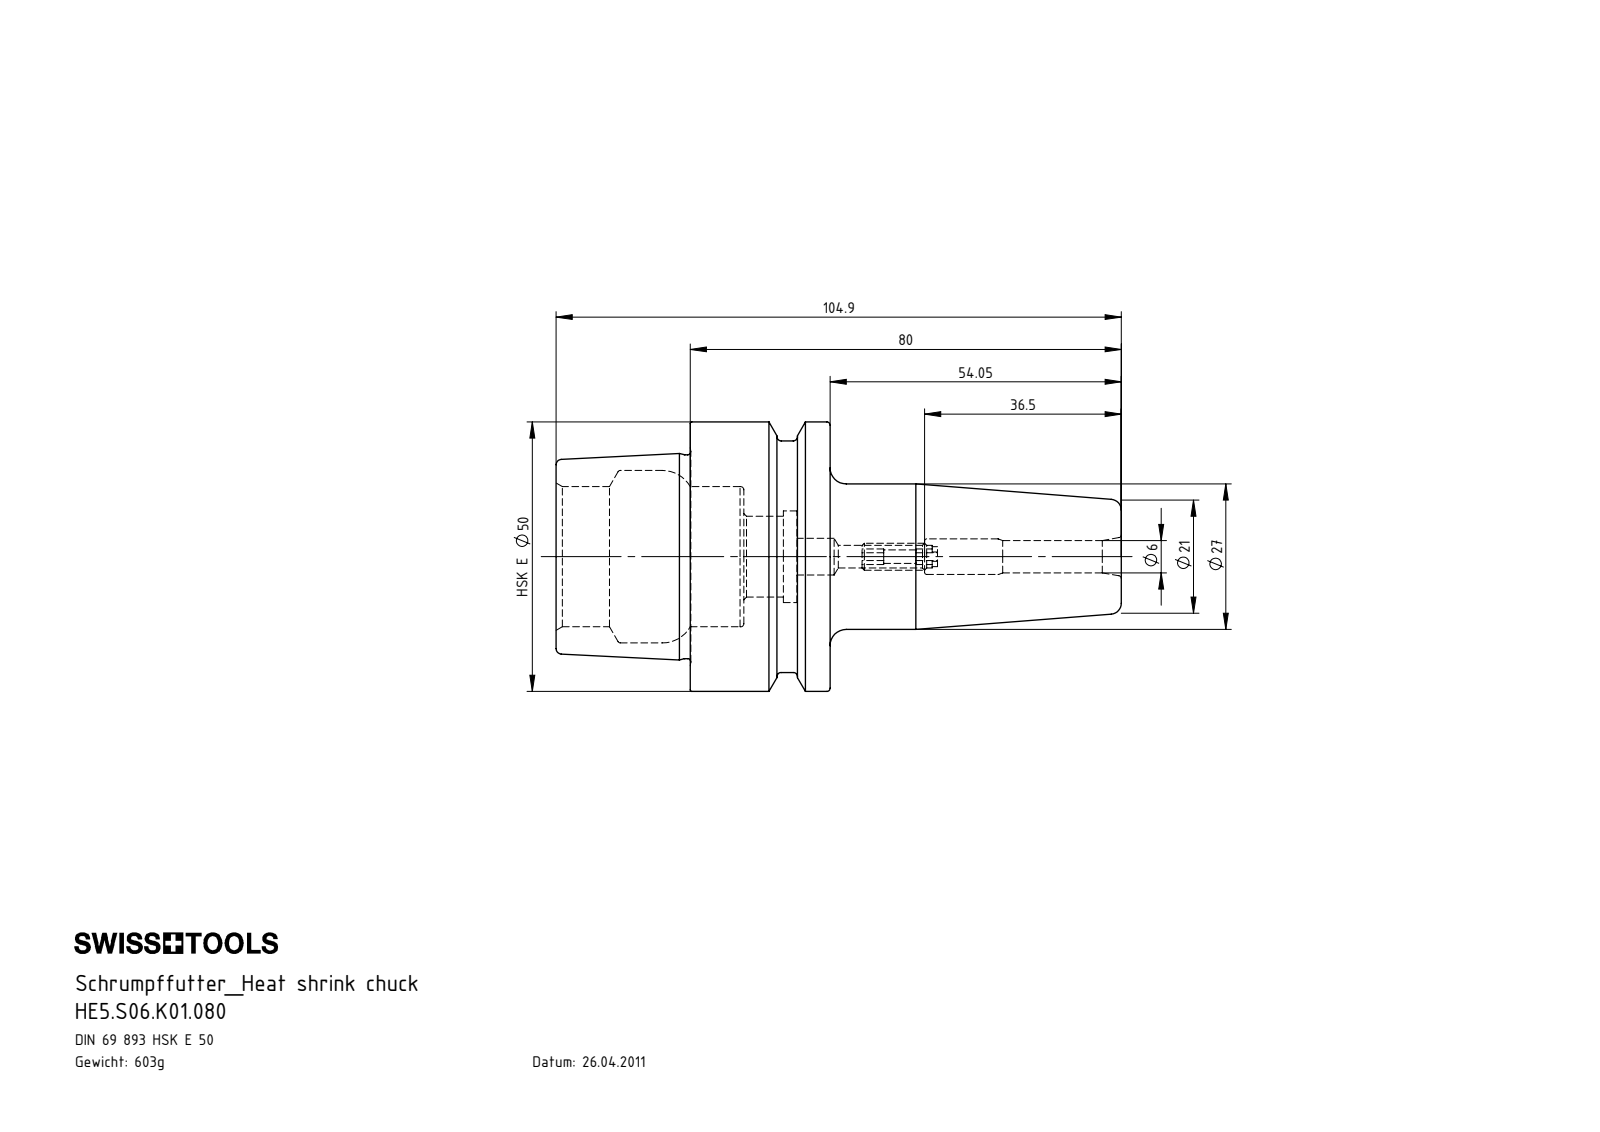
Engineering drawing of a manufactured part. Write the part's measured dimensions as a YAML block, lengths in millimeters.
part_name: "HE5.S06.K01.080; ERU-AN1.K01.014_A; HE5-S06.K01.080_B_Fertigbearbeitung"
step_written_by: "SolidWorks 2017 (AUTOMOTIVE_DESIGN)"
units: millimeters
bodies: {solids: 2, faces: 142, planar: 43, cylindrical: 34, other: 65}
overall_size: [104.9, 50, 50]
volume: 76828
surface_area: 20286
round_holes:
  - {diameter: 2.5, count: 1}
  - {diameter: 4.2, count: 1}
  - {diameter: 6, count: 1}
  - {diameter: 6.6, count: 1}
  - {diameter: 6.8, count: 1}
  - {diameter: 15, count: 1}
  - {diameter: 17, count: 1}
  - {diameter: 26, count: 1}
  - {diameter: 32, count: 1}
round_bosses_or_shafts:
  - {diameter: 50, count: 1}
  - {diameter: 42.95, count: 1}
  - {diameter: 37.81, count: 1}
  - {diameter: 27, count: 1}
  - {diameter: 5, count: 1}
face_to_face_distances: [25.95, 24.9, 50.85, 9.95, 34.85, 16, 44.7, 19.8, 9.85, 6.15]
